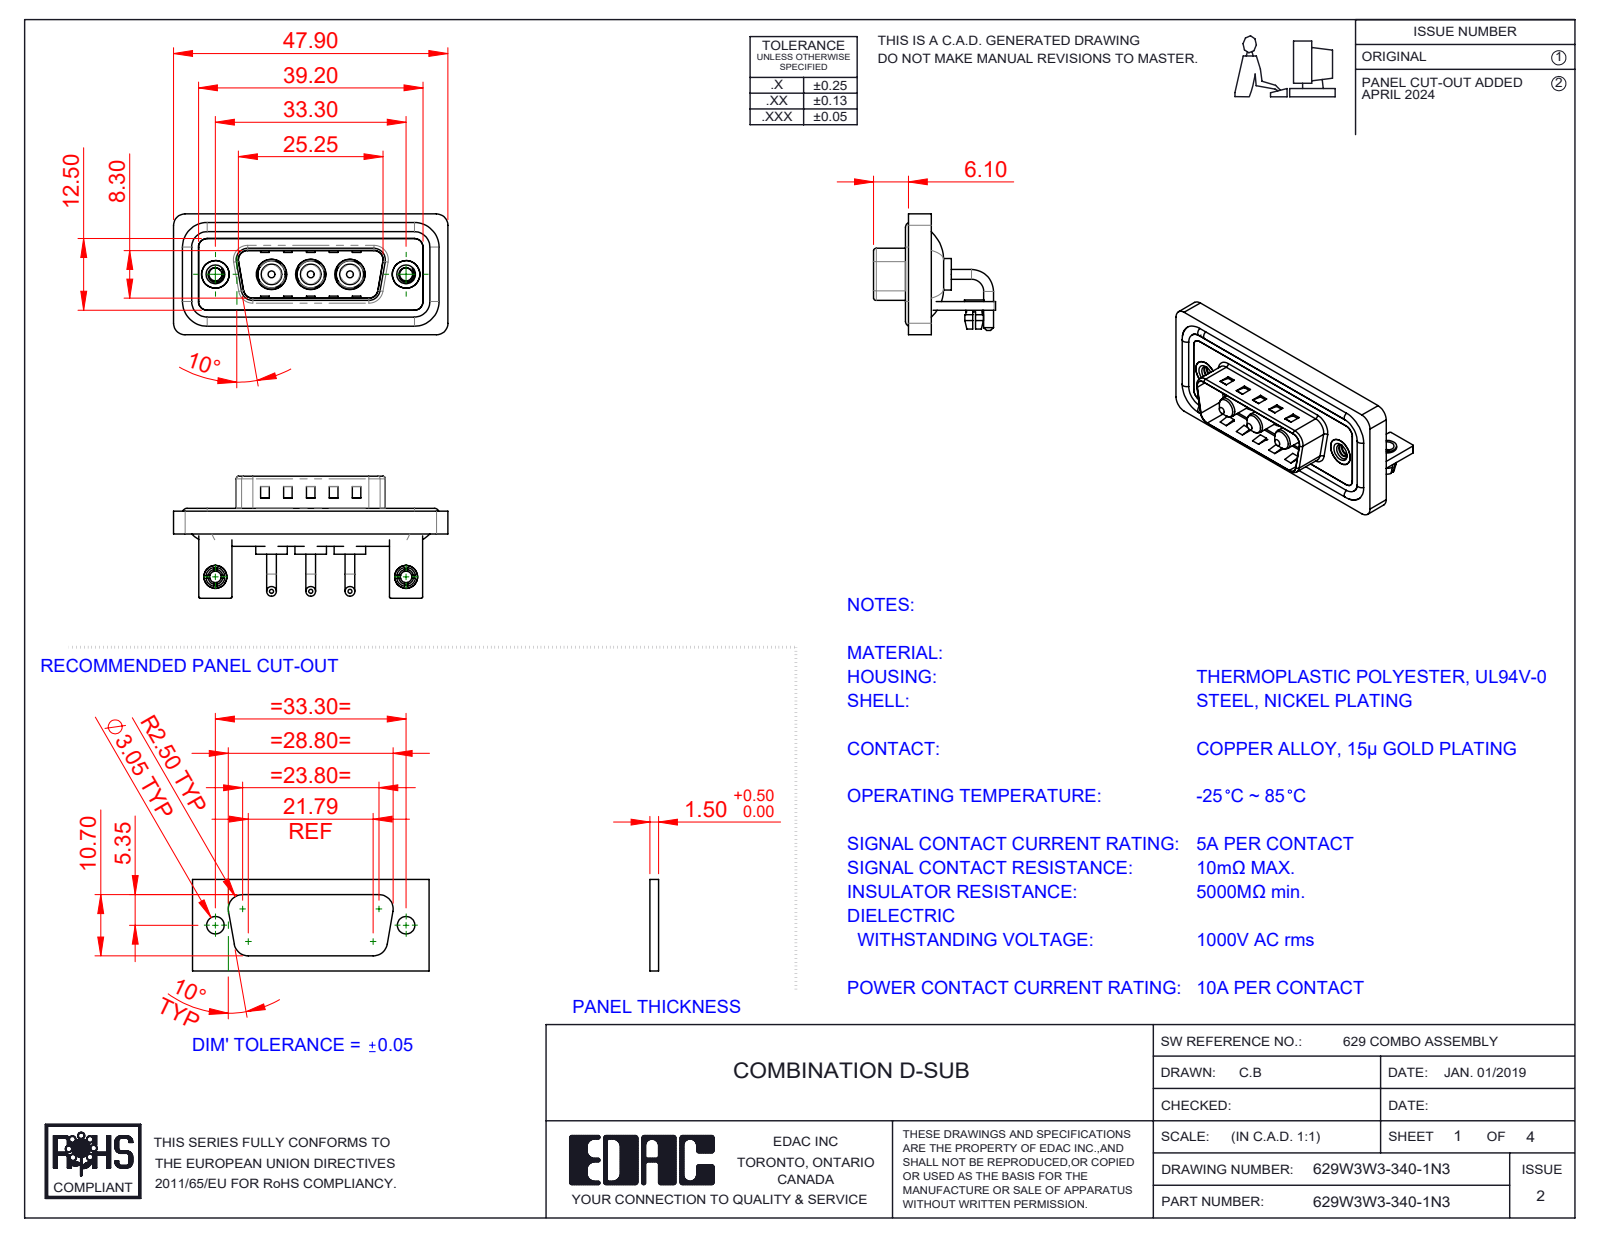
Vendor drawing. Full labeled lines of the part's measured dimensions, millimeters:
Part name (STEP PRODUCT): 629Combo Shell Front_15 Contacts; 629Combo Housing_3W3; Power Pin_10A RA; 629Combo Board Lock (+5 more)
STEP written by: SolidWorks 2023 (CONFIG_CONTROL_DESIGN)
Units: millimetres
Bodies: 17 solids, 708 faces (275 planar, 297 cylindrical, 136 other)
Overall size (bounding box): 47.9 × 21.3 × 21.1
Volume: 5 918 mm³ · Surface area: 9 681 mm²
Round holes (diameter × count): ⌀4.85 ×3, ⌀5.3 ×3, ⌀2 ×2, ⌀2.26 ×2, ⌀2.5 ×2, ⌀3.2 ×2, ⌀4 ×2, ⌀4.8 ×2, ⌀5 ×2
Round bosses / shafts (diameter × count): ⌀1.7 ×6, ⌀1.6 ×4, ⌀5.5 ×3, ⌀5.2 ×3, ⌀4.75 ×3, ⌀3.75 ×3, ⌀3.6 ×3, ⌀4.9 ×2
Partial cylindrical surfaces — rounded edges, fillets, slot ends (radius × count): R2 ×21, R1.5 ×18, R0.25 ×16, R0.5 ×9, R1.6 ×8, R0.6 ×4, R0.65 ×4, R0.9 ×4
Main face-to-face distances: 0.4, 1.5, 0.8, 2.9, 1.1, 2.1, 3.7, 1.6, 1.2, 4.5
Hole centre spacings: 6.85, 9.8, 16.65, 23.5, 33.3, 13.7
